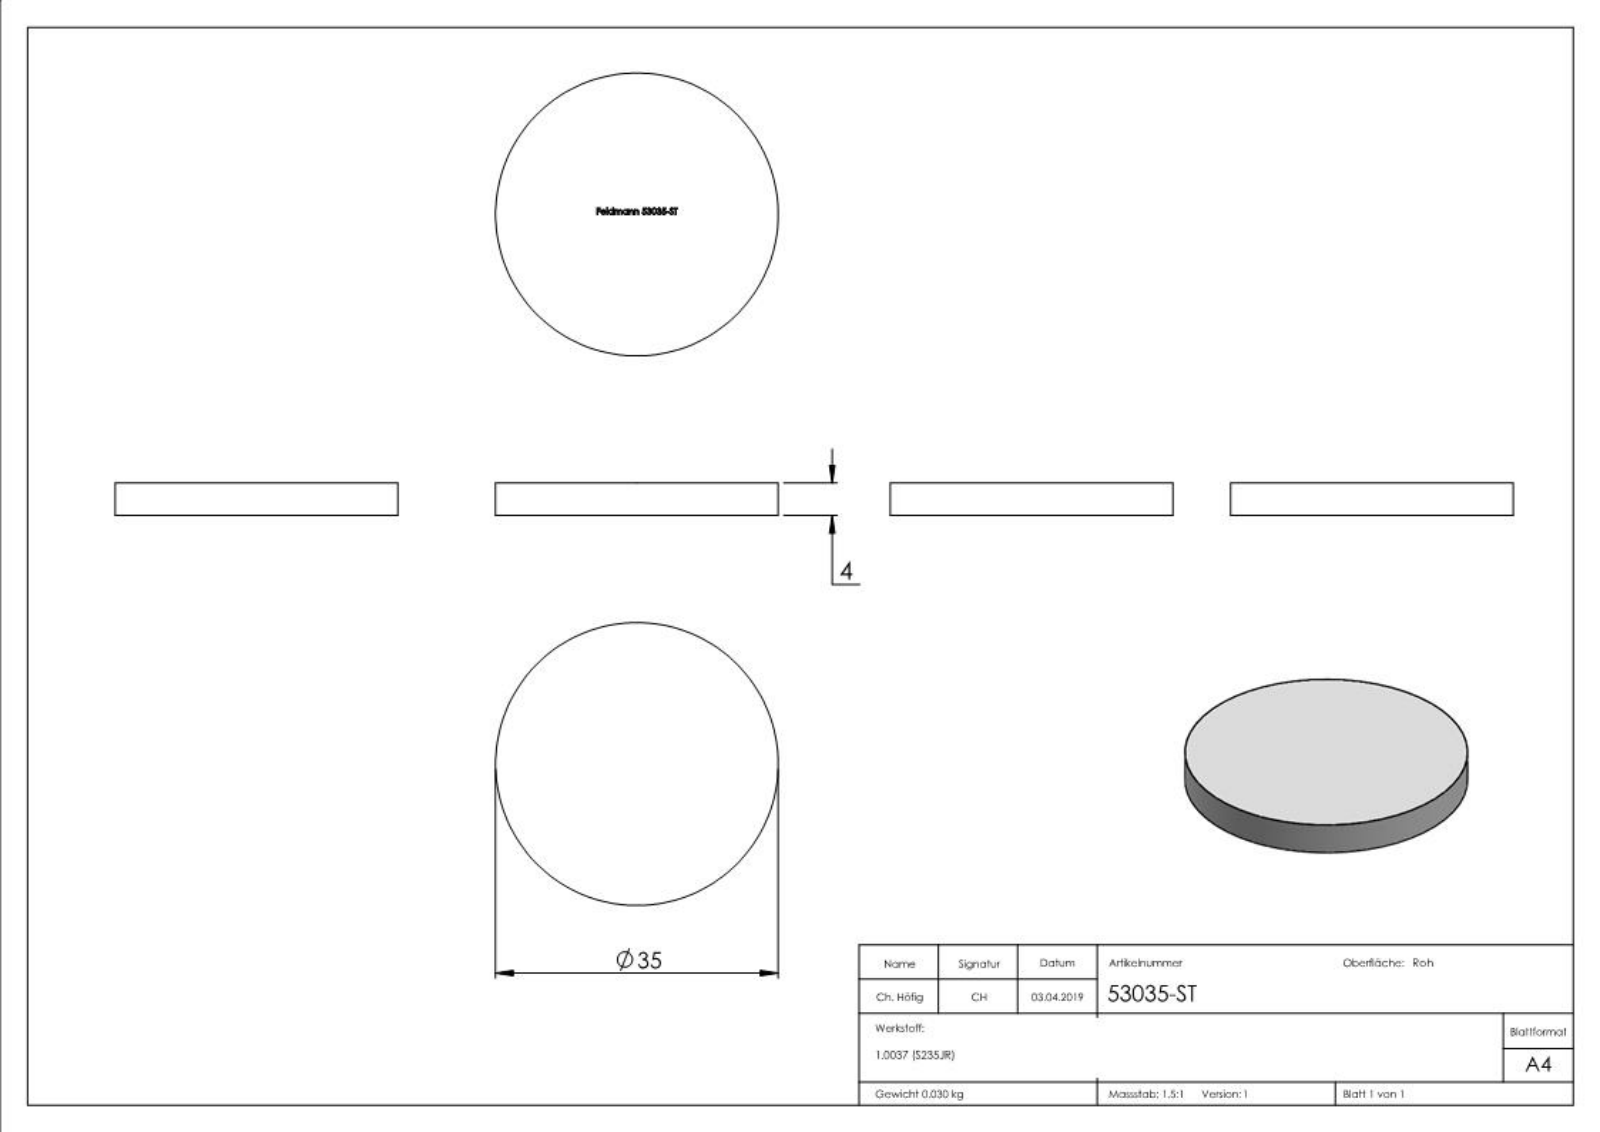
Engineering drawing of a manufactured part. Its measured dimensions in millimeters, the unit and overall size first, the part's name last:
Units: millimetres
Overall size (bounding box): 35 × 35 × 4
Round bosses / shafts (diameter × count): ⌀35 ×1
Main face-to-face distances: 4, 3.9, 0.44, 0.99, 1.78, 0.67, 0.79, 1.21, 8.49, 9.7
Volume: 3 848 mm³ · Surface area: 2 369 mm²
Bodies: 1 solid, 226 faces (108 planar, 2 cylindrical, 116 other)
Part name (STEP PRODUCT): 53035-ST
STEP written by: SolidWorks 2015 (CONFIG_CONTROL_DESIGN)
